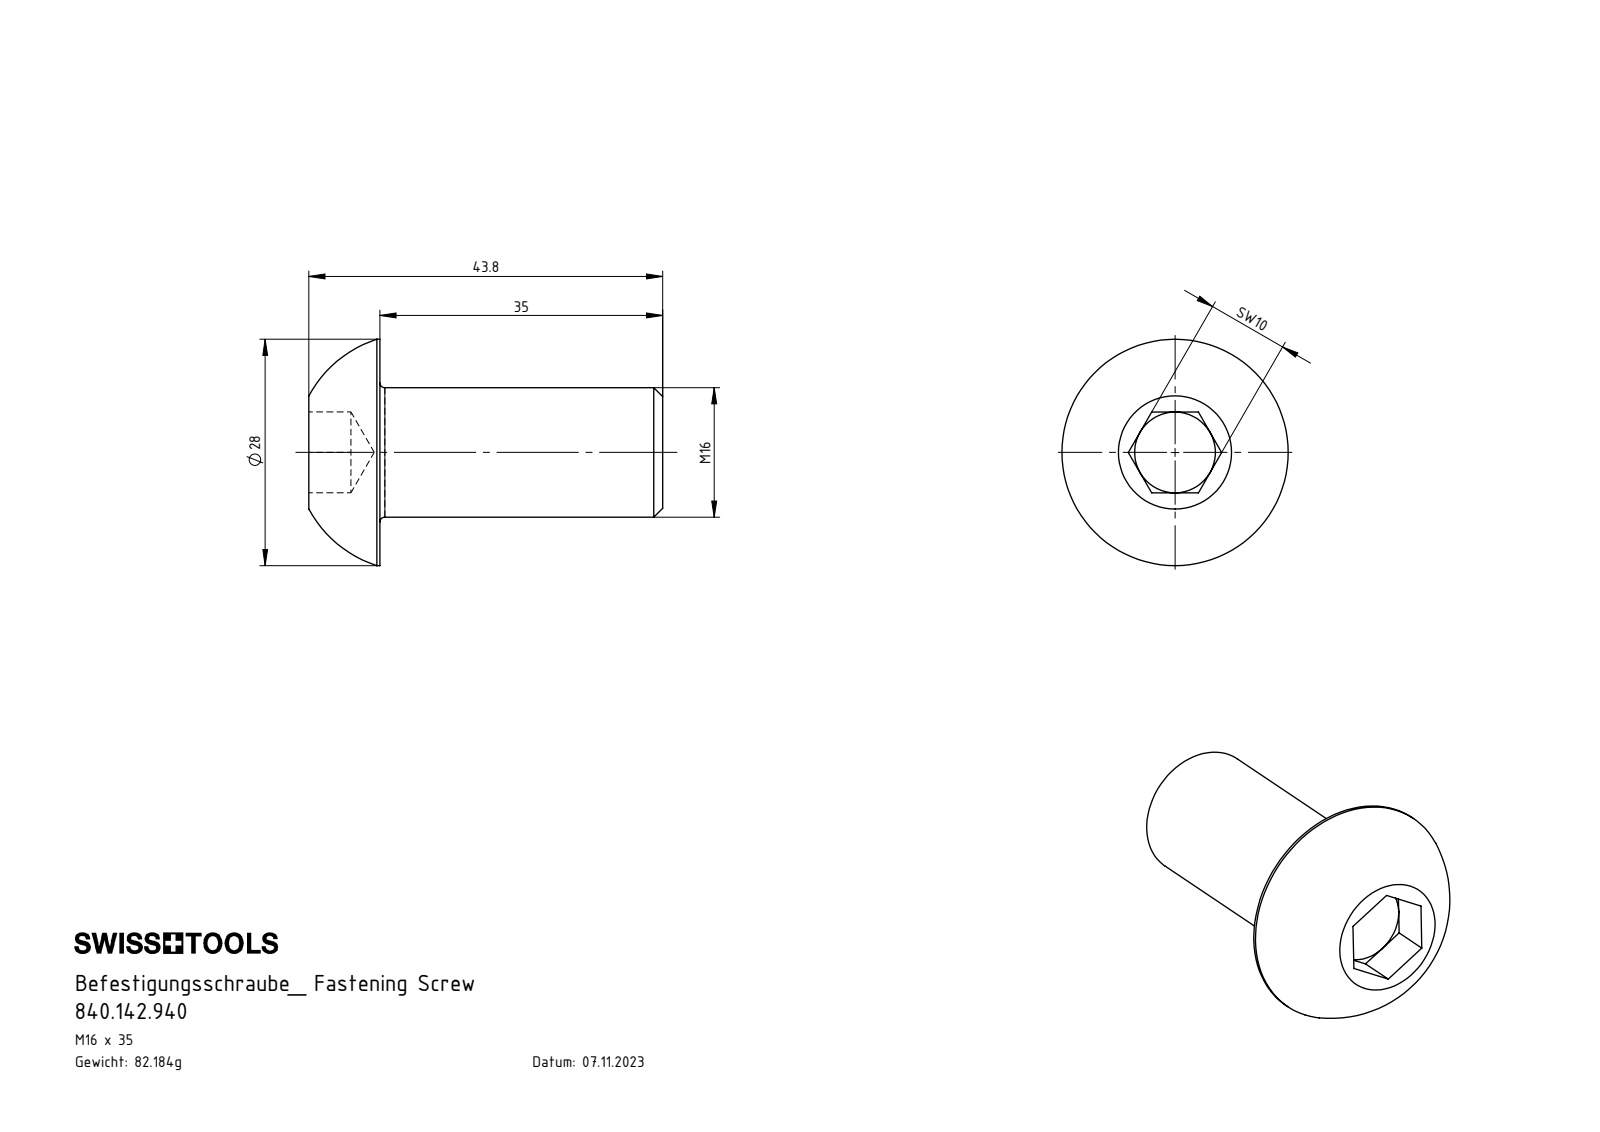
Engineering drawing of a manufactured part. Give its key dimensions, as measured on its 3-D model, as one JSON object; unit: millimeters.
{"part_name": "840.142.940", "step_written_by": "SolidWorks 2022 (AUTOMOTIVE_DESIGN)", "units": "millimeters", "bodies": {"solids": 1, "faces": 27, "planar": 15, "cylindrical": 4, "other": 8}, "overall_size": [43.8, 28, 28], "volume_mm3": 10273, "surface_area_mm2": 3486, "round_bosses_or_shafts": [[28, 1], [16, 1]], "face_to_face_distances": [35, 10, 8.8, 43.8, 5.2, 3.6, 38.6]}
